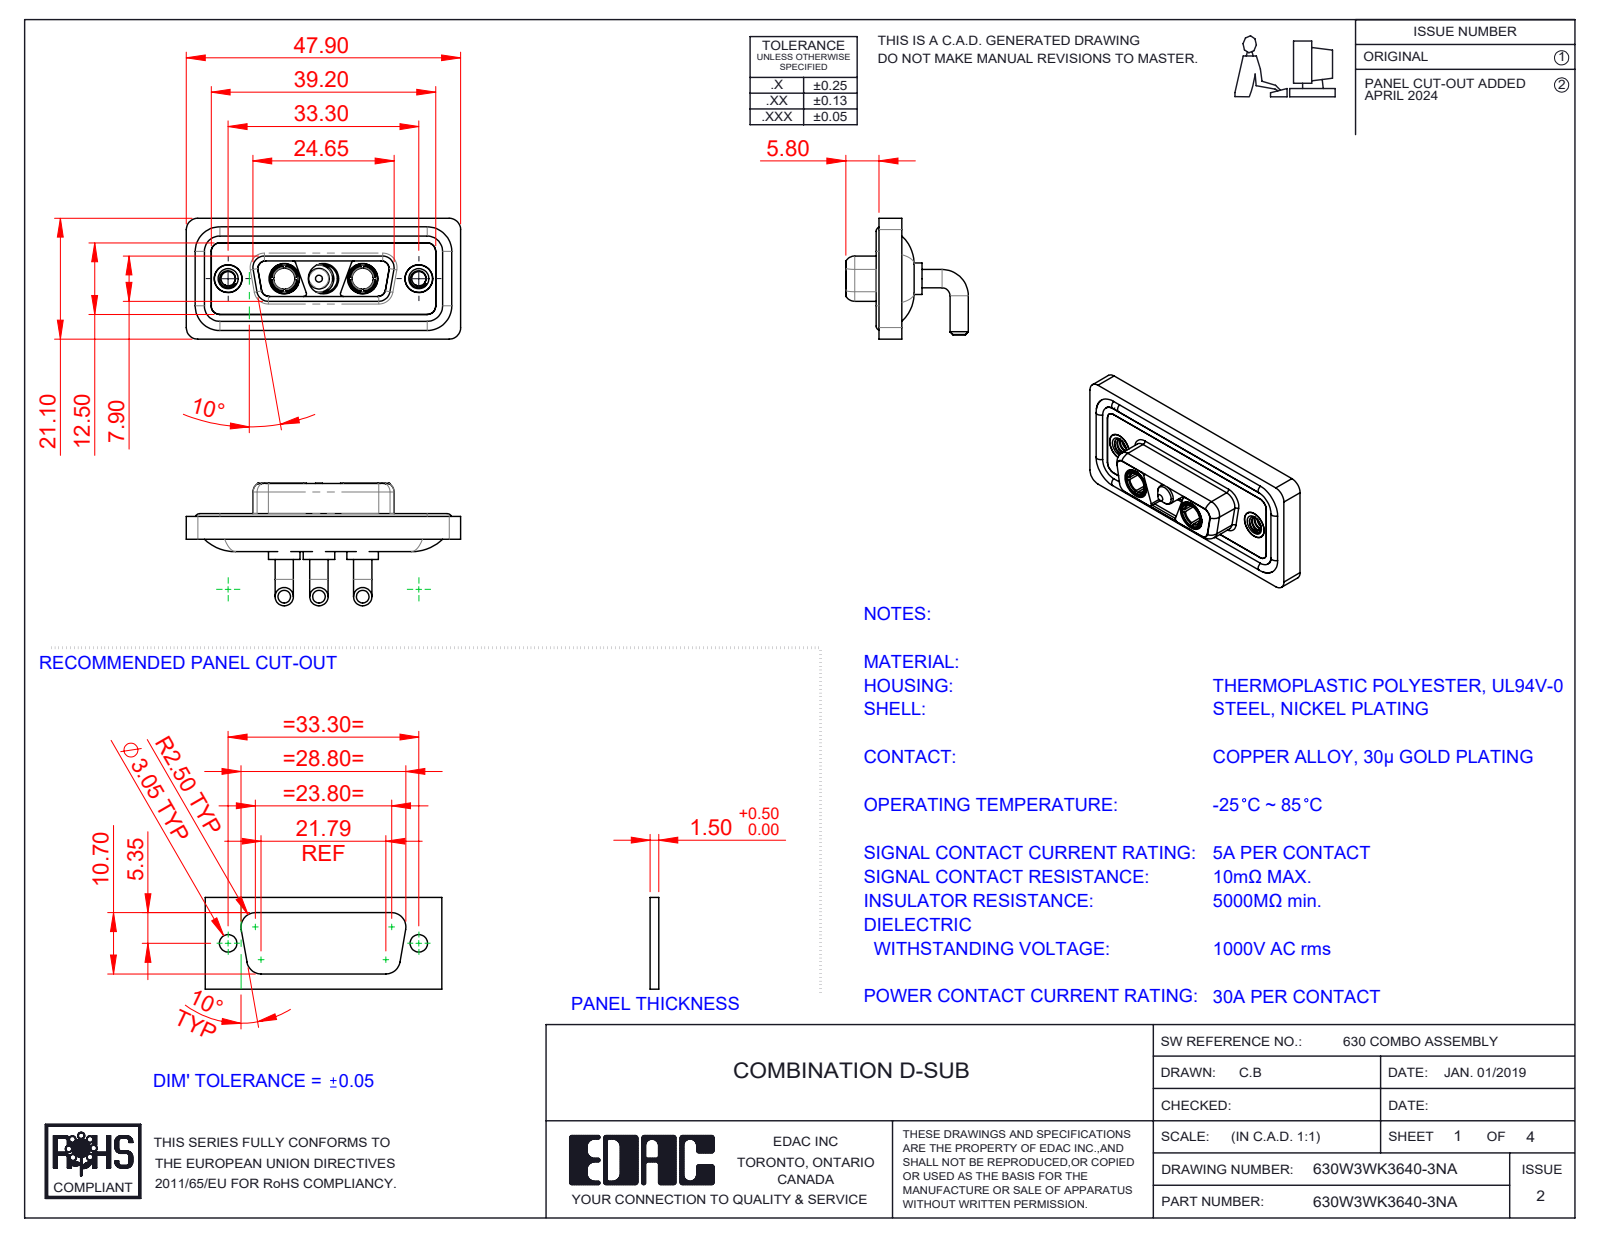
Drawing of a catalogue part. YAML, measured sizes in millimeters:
part_name: "630Combo Housing_3WK3; 630Combo Shell Rear_15 Contacts; Power Pin_30A RA; 630Combo Threaded Rivet_A (+4 more)"
step_written_by: "SolidWorks 2023 (CONFIG_CONTROL_DESIGN)"
units: millimeters
bodies: {solids: 13, faces: 589, planar: 178, cylindrical: 262, other: 149}
overall_size: [47.9, 21.4, 21.1]
volume: 6109
surface_area: 9797
round_holes:
  - {diameter: 4.85, count: 5}
  - {diameter: 5.3, count: 3}
  - {diameter: 2.5, count: 2}
  - {diameter: 3.7, count: 2}
  - {diameter: 4, count: 2}
  - {diameter: 4.05, count: 2}
  - {diameter: 5, count: 2}
round_bosses_or_shafts:
  - {diameter: 3.2, count: 6}
  - {diameter: 1.6, count: 4}
  - {diameter: 5.5, count: 3}
  - {diameter: 5.2, count: 3}
  - {diameter: 4.75, count: 3}
  - {diameter: 3.75, count: 3}
  - {diameter: 4.96, count: 2}
  - {diameter: 4.95, count: 2}
partial_cylinders:
  - {radius: 2, count: 20}
  - {radius: 1.5, count: 18}
  - {radius: 1.35, count: 12}
  - {radius: 0.5, count: 8}
  - {radius: 1.6, count: 8}
  - {radius: 0.25, count: 4}
  - {radius: 0.6, count: 4}
  - {radius: 0.65, count: 4}
face_to_face_distances: [0.4, 1.8, 1.1, 1.6, 2.9, 2.5, 3.1, 3.7, 4.1, 1.5]
hole_center_spacings: [6.85, 9.8, 16.65, 23.5, 13.7, 33.3]
